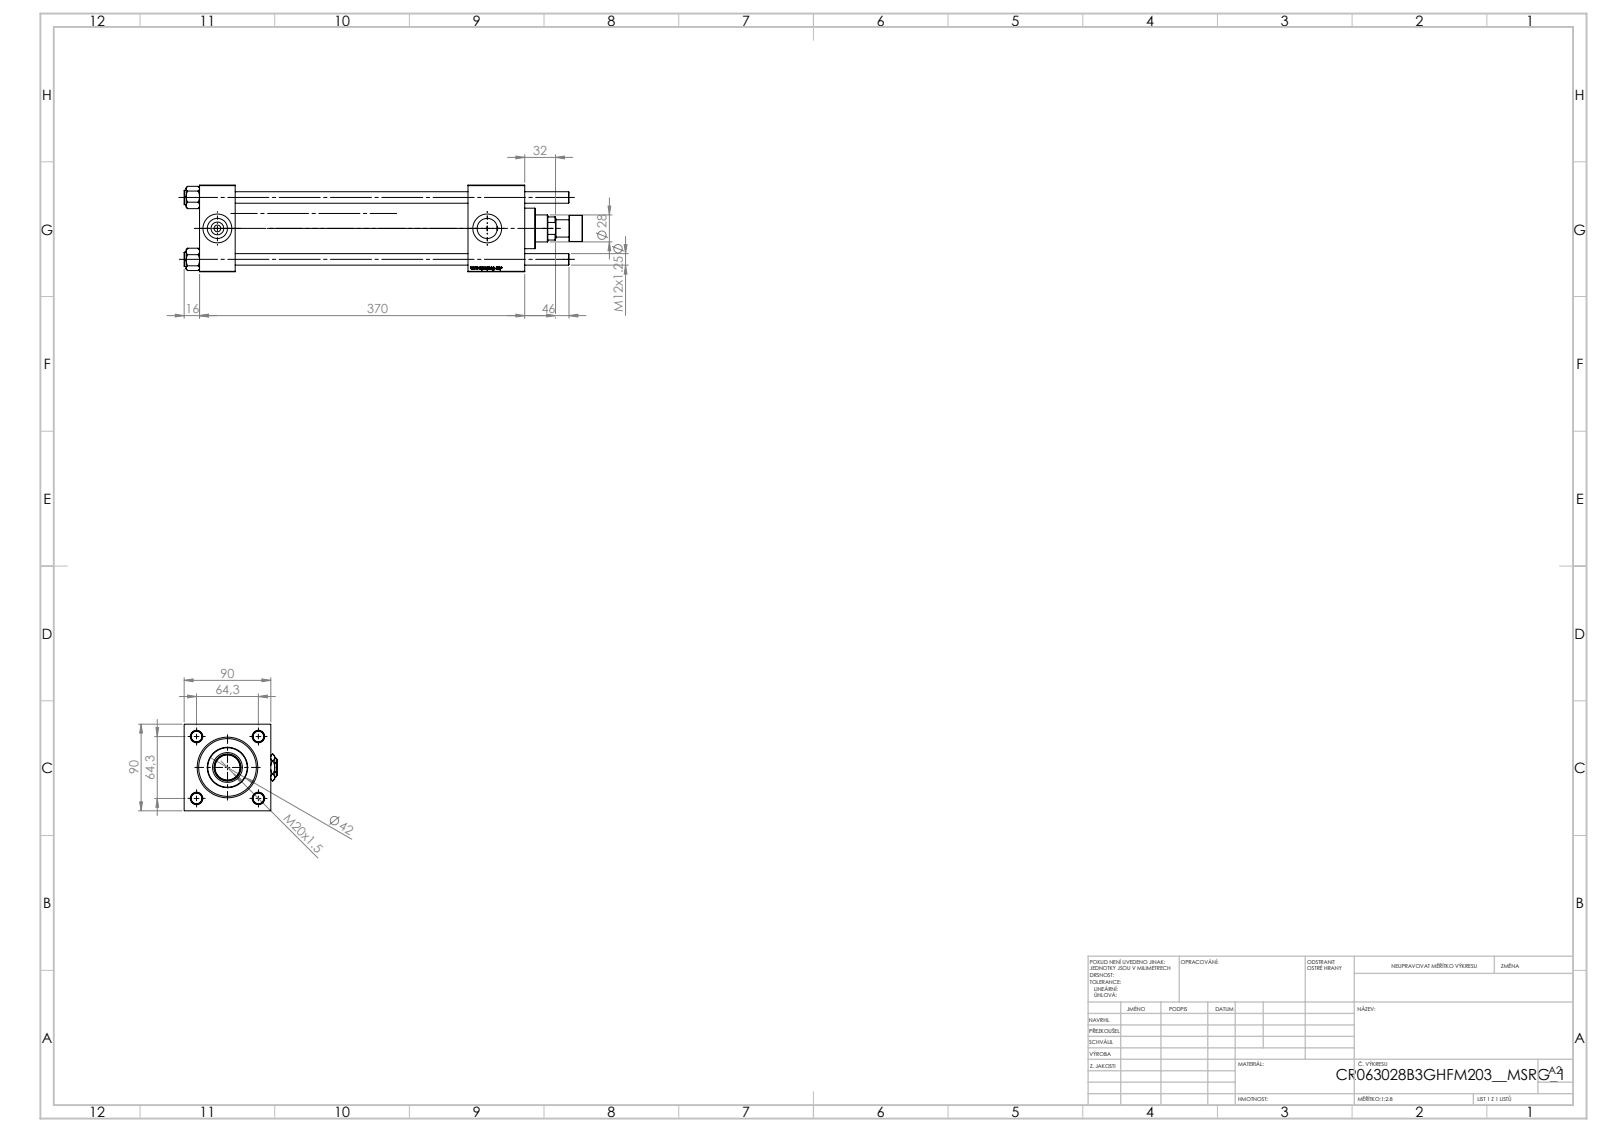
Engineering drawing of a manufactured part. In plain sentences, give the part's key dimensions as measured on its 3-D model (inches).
The part is named "V215CR_B-1; NUT_M5_B; V215_VC_A; V215CR_B_TYCINKA (+3 more)". Its 3-D file was written by "SolidWorks 2019 (CONFIG_CONTROL_DESIGN)". It is 14 solids with 1271 faces: 483 planar, 92 cylindrical and 696 other. Overall it measures 16.299 by 3.819 by 3.543 inches. Its volume is 79.09 cubic inches and its surface area 500.1 square inches. Round holes: 4 of diameter 0.472, 2 of diameter 0.276, 2 of diameter 0.825, 2 of diameter 1.181, 1 of diameter 0.728, 1 of diameter 1.102, 1 of diameter 1.22, 1 of diameter 1.969, 1 of diameter 2.362, 1 of diameter 2.48. Round bosses or shafts: 4 of diameter 0.591, 1 of diameter 2.717, 1 of diameter 1.654, 1 of diameter 1.063, 1 of diameter 0.709. The main face-to-face distances are 3.543, 1.457, 11.85, 13.307, 2.323, 10.984, 9.528, 12.177, 10.72, 1.193. The hole center spacings are 1.79, 2.531, 3.58, 11.043.
